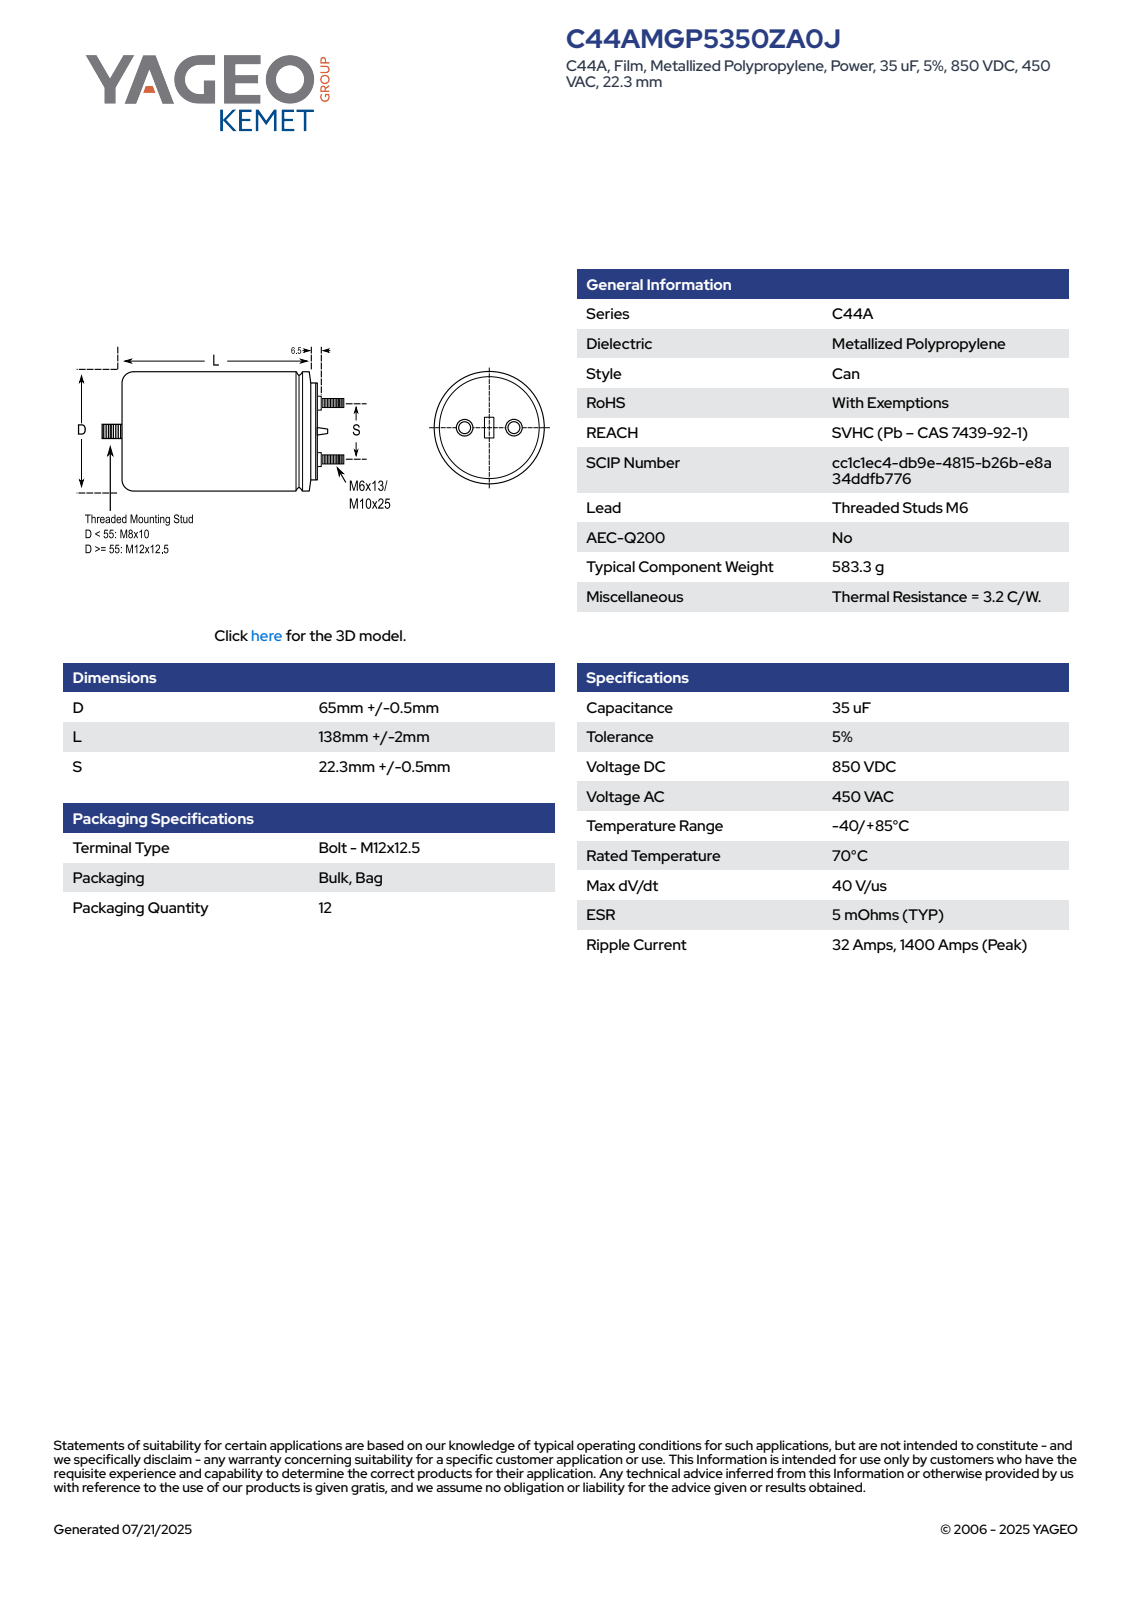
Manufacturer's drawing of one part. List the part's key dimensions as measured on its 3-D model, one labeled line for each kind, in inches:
Part name (STEP PRODUCT): CFP_C44A_65X138_D65.5L140S22.3
STEP written by: SolidWorks 2014 (AUTOMOTIVE_DESIGN)
Units: inches
Bodies: 1 solid, 102 faces (29 planar, 34 cylindrical, 39 other)
Overall size (bounding box): 6.772 × 2.579 × 2.579
Volume: 29.33 in³ · Surface area: 57.32 in²
Round bosses / shafts (diameter × count): ⌀0.354 ×2, ⌀0.236 ×2, ⌀2.579 ×1, ⌀2.022 ×1, ⌀0.472 ×1
Partial cylindrical surfaces — rounded edges, fillets, slot ends (radius × count): R1.289 ×1
Main face-to-face distances: 5.709, 0.492, 6.201, 6.26, 5.768, 0.059, 6.772, 6.28, 0.571, 0.512
